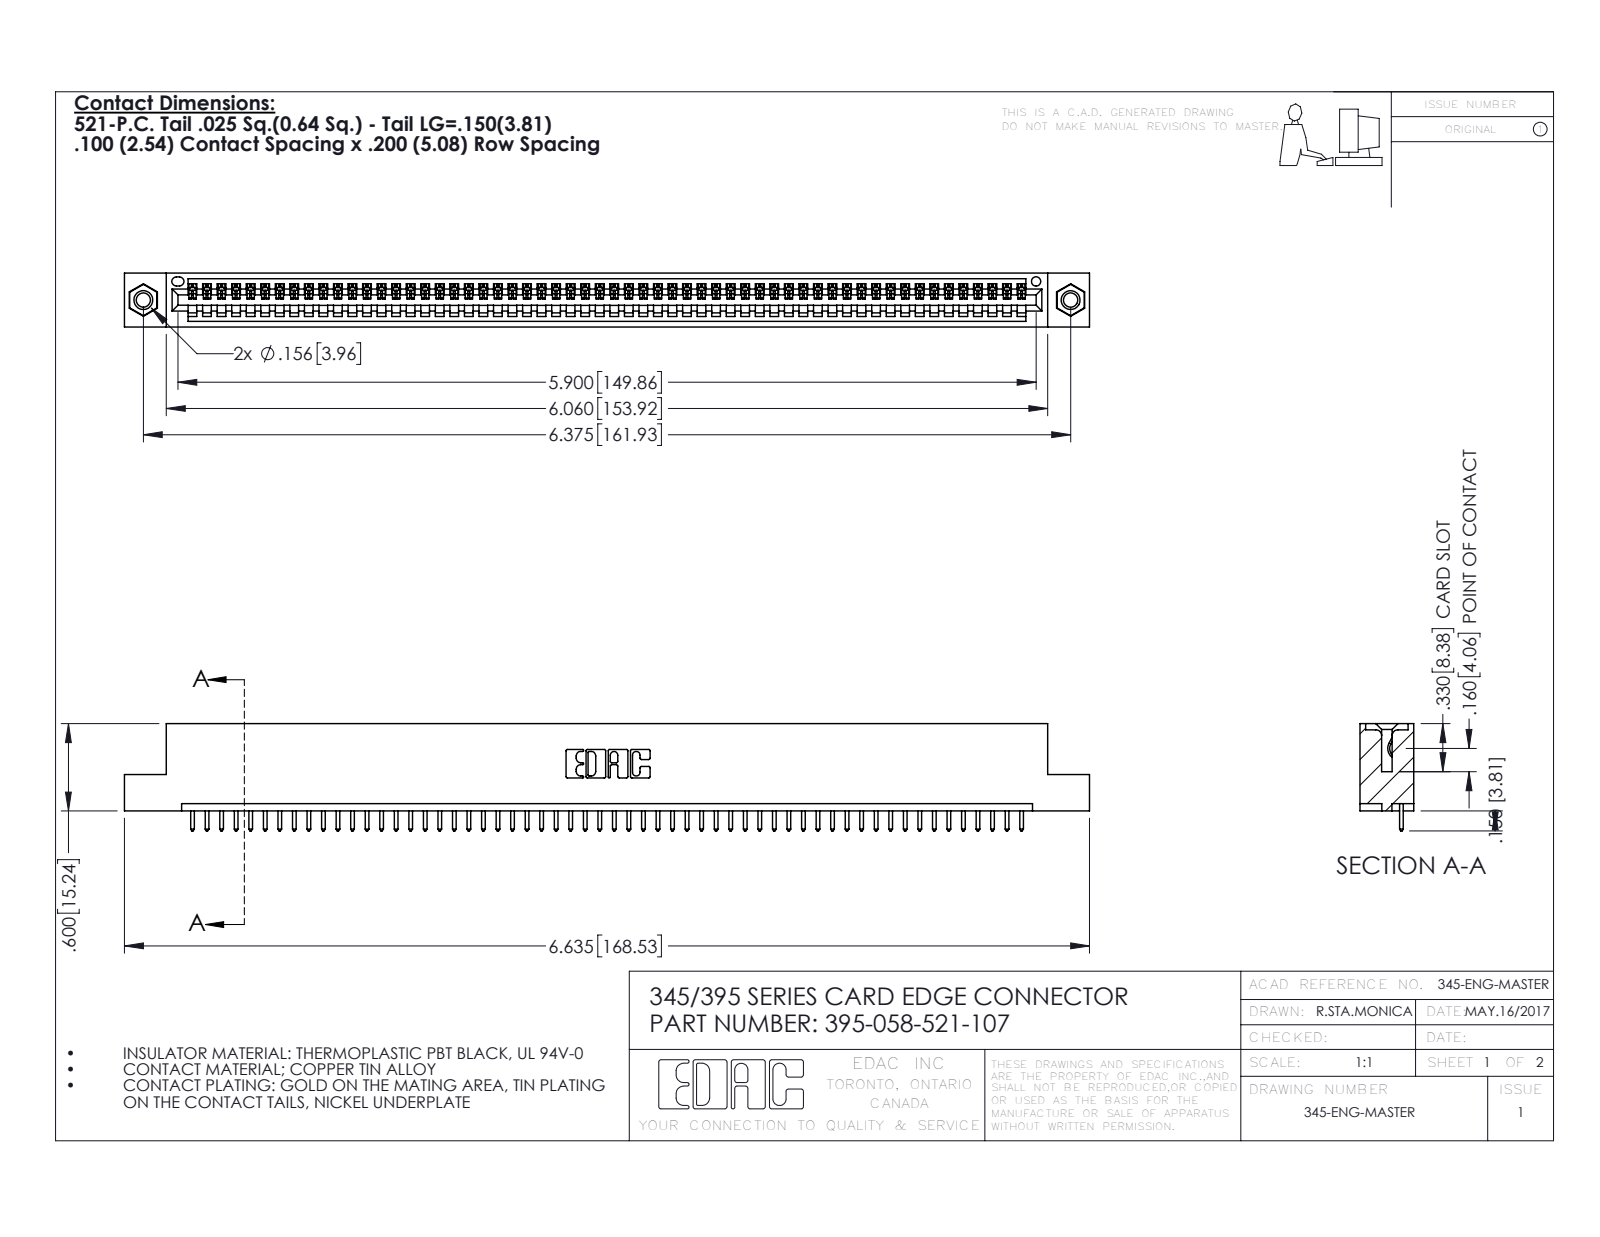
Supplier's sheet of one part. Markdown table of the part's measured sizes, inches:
| quantity | value |
| --- | --- |
| part name | 345-250-001_345-250-005-103; 395-058-521-107; 345-292-001_345-293-121; 345 Part_Flush Mounting Lugs - 0.156 Dia-TI |
| STEP written by | SolidWorks 2016 (CONFIG_CONTROL_DESIGN) |
| units | inches |
| bodies | 61 solids, 3550 faces (2432 planar, 1102 cylindrical, 16 other) |
| overall size | 6.635 × 0.737 × 0.37 |
| volume | 0.974 in³ |
| surface area | 32.26 in² |
| round holes (diameter × count) | 0.098 × 2, 0.125 × 2, 0.156 × 2, 0.064 × 1 |
| round bosses / shafts (diameter × count) | 0.155 × 2 |
| partial cylindrical surfaces (radius × count) | 0.006 × 116, 0.01 × 116, 0.01 × 22, 0.007 × 6, 0.031 × 6, 0.026 × 3, 0.031 × 2, 0.04 × 2 |
| main face-to-face distances | 0.072, 0.298, 0.37, 0.2, 0.098, 0.272, 0.025, 0.225, 0.149, 0.072 |
| hole center spacings | 0.27, 6.139, 6.375 |
